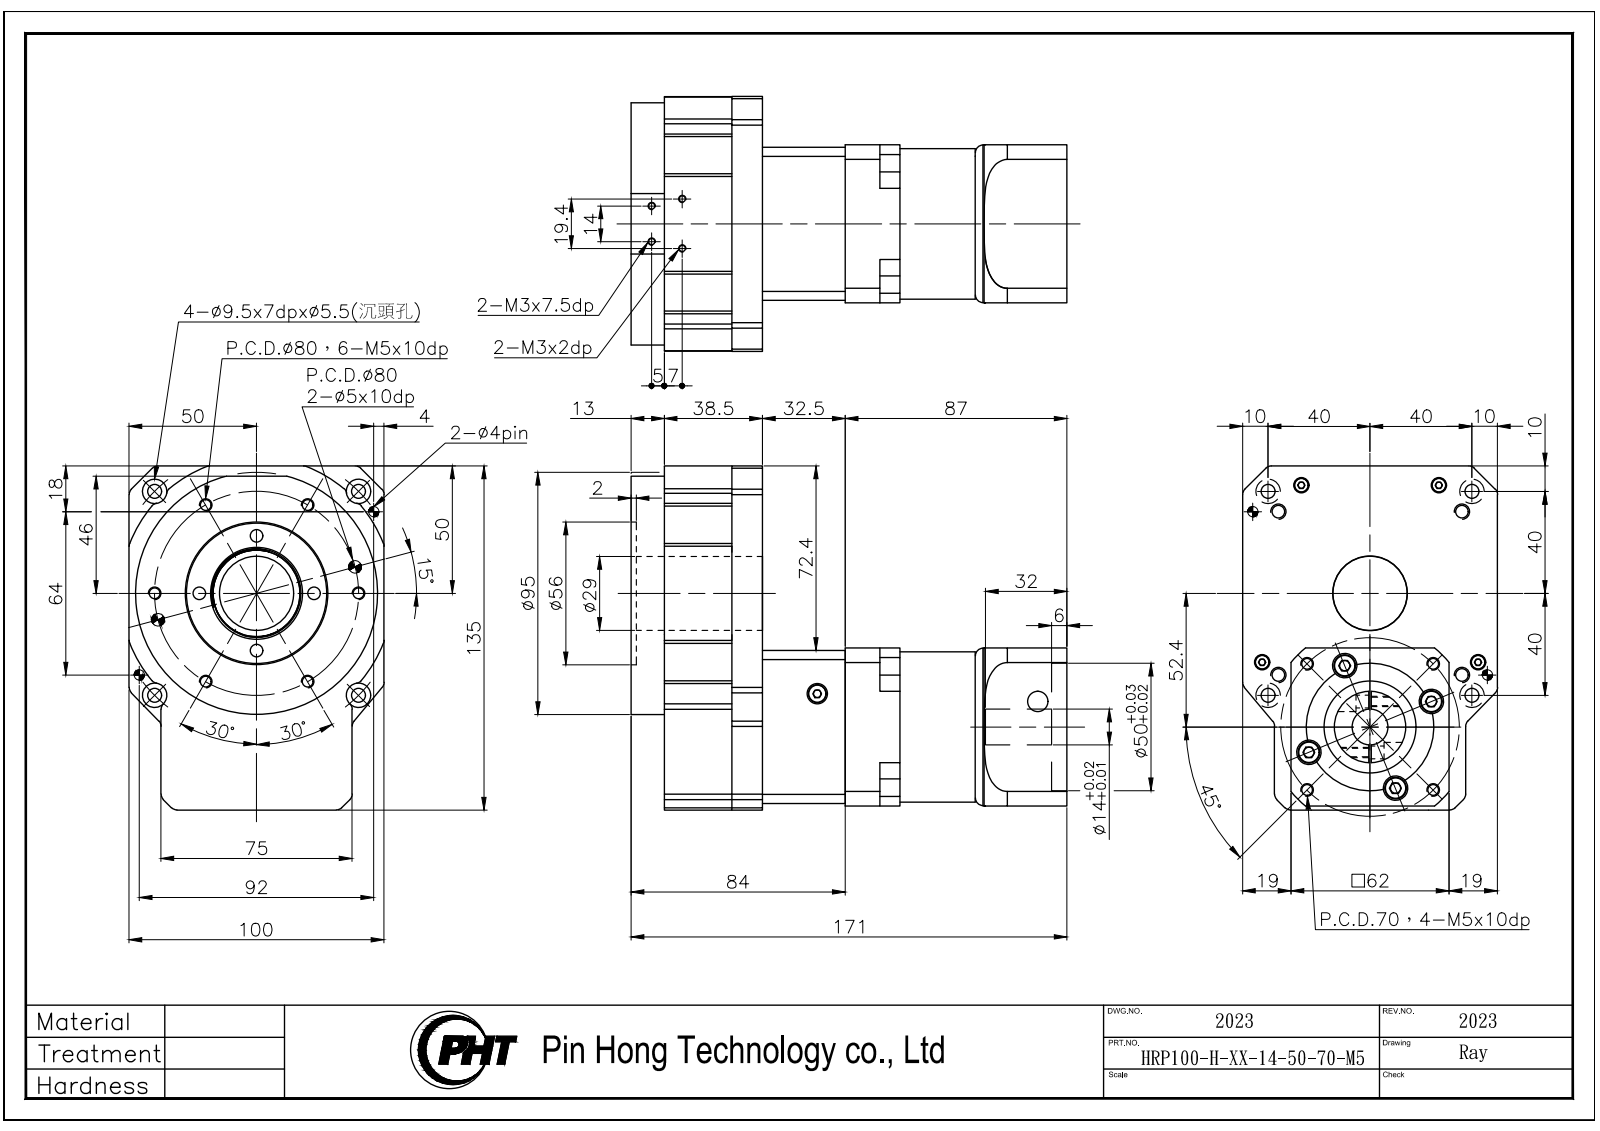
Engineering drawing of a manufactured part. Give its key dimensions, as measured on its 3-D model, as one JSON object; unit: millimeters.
{"part_name": "HRP100-H-XX-14-50-70-M5_2023", "step_written_by": "SolidWorks 2016 (CONFIG_CONTROL_DESIGN)", "units": "millimeters", "bodies": {"solids": 1, "faces": 593, "planar": 238, "cylindrical": 279, "other": 76}, "overall_size": [171, 135, 100], "volume_mm3": 845077, "surface_area_mm2": 113126, "round_holes": [[4.2, 10], [5, 10], [5.2, 8], [8, 8], [9.5, 8], [4.5, 5], [2.5, 4], [3.4, 4], [5.5, 4], [6, 4], [3.3, 2], [4, 2]], "round_bosses_or_shafts": [[8.5, 4], [7, 4], [5.5, 4], [95, 1], [61.8, 1], [59, 1], [55, 1], [28, 1]], "partial_cylinders_radius": [[3, 30], [4.8, 4], [5, 4], [2.5, 1], [3.9, 1], [34, 1], [40, 1], [53.5, 1]], "face_to_face_distances": [1, 61, 62, 38.5, 51.5, 60, 81, 13, 19, 12.5], "hole_center_spacings": [43.66, 74.2, 26, 80, 8.94, 10, 13.22, 14.82]}
